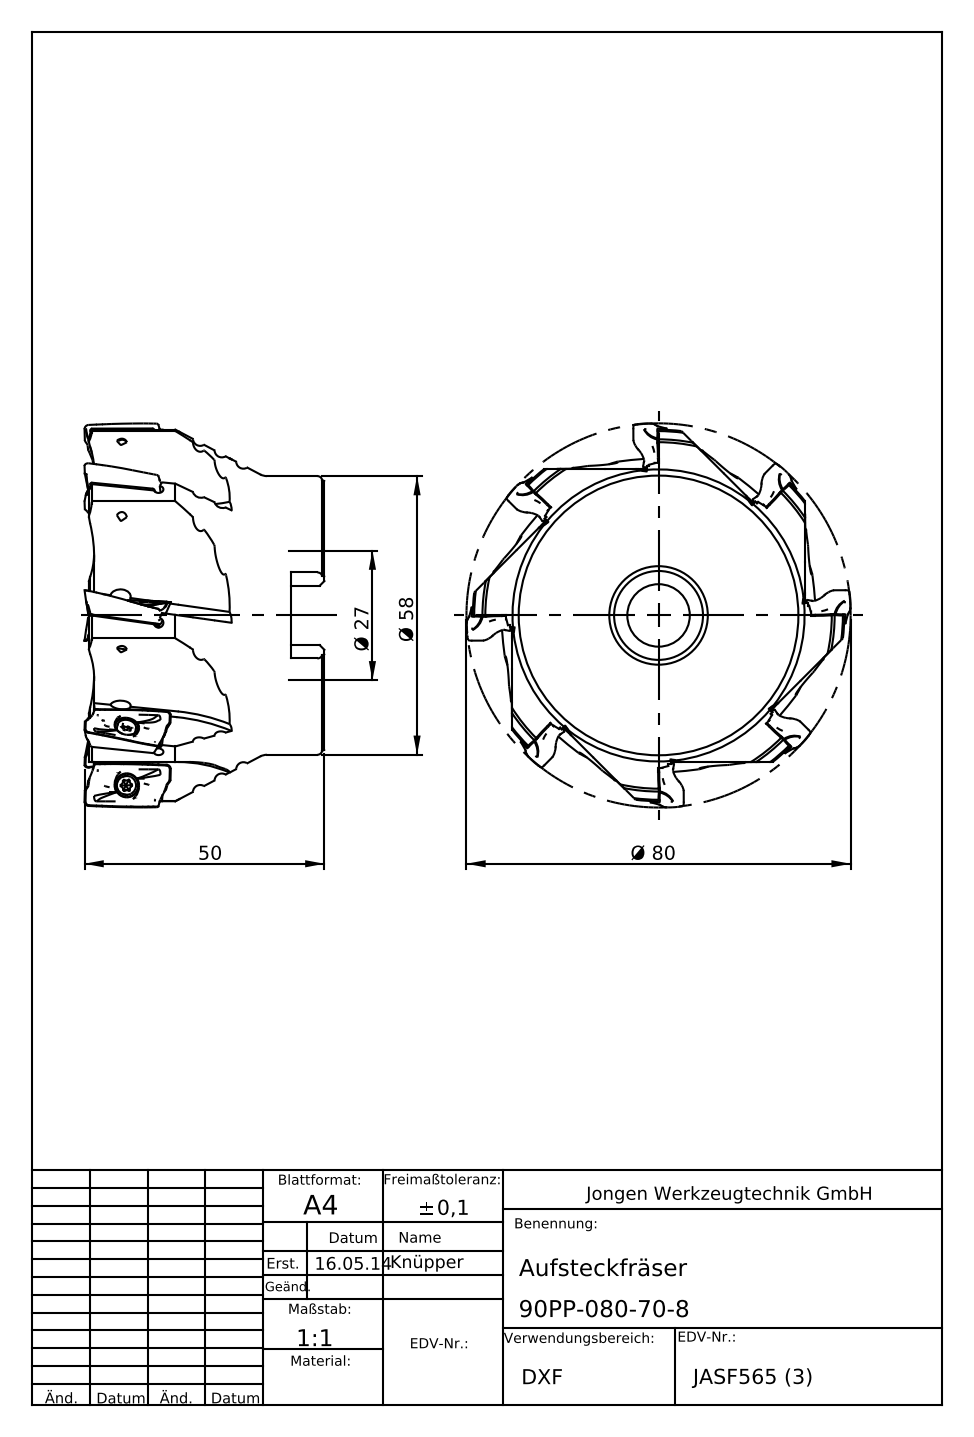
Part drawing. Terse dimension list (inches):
name: 90PP-080-70-8
written by: SolidWorks 2019 (AUTOMOTIVE_DESIGN)
unit: in
bodies: 1 solid, 441 faces (98 planar, 103 cylindrical, 240 other)
size: 3.147 × 3.147 × 1.969
volume: 9.333 in³; area: 39.83 in²
holes: 8× ⌀0.079, 8× ⌀0.118, 1× ⌀0.512, 1× ⌀0.728, 1× ⌀1.063, 1× ⌀1.069, 1× ⌀1.075
bosses: 1× ⌀2.283
rounds: 8× R0.197, 8× R1.102, 1× R1.184, 1× R1.522
face distances: 1.874, 0.276, 1.598, 0.984, 0.709, 0.89, 2.402, 0.957, 1.445, 0.488
